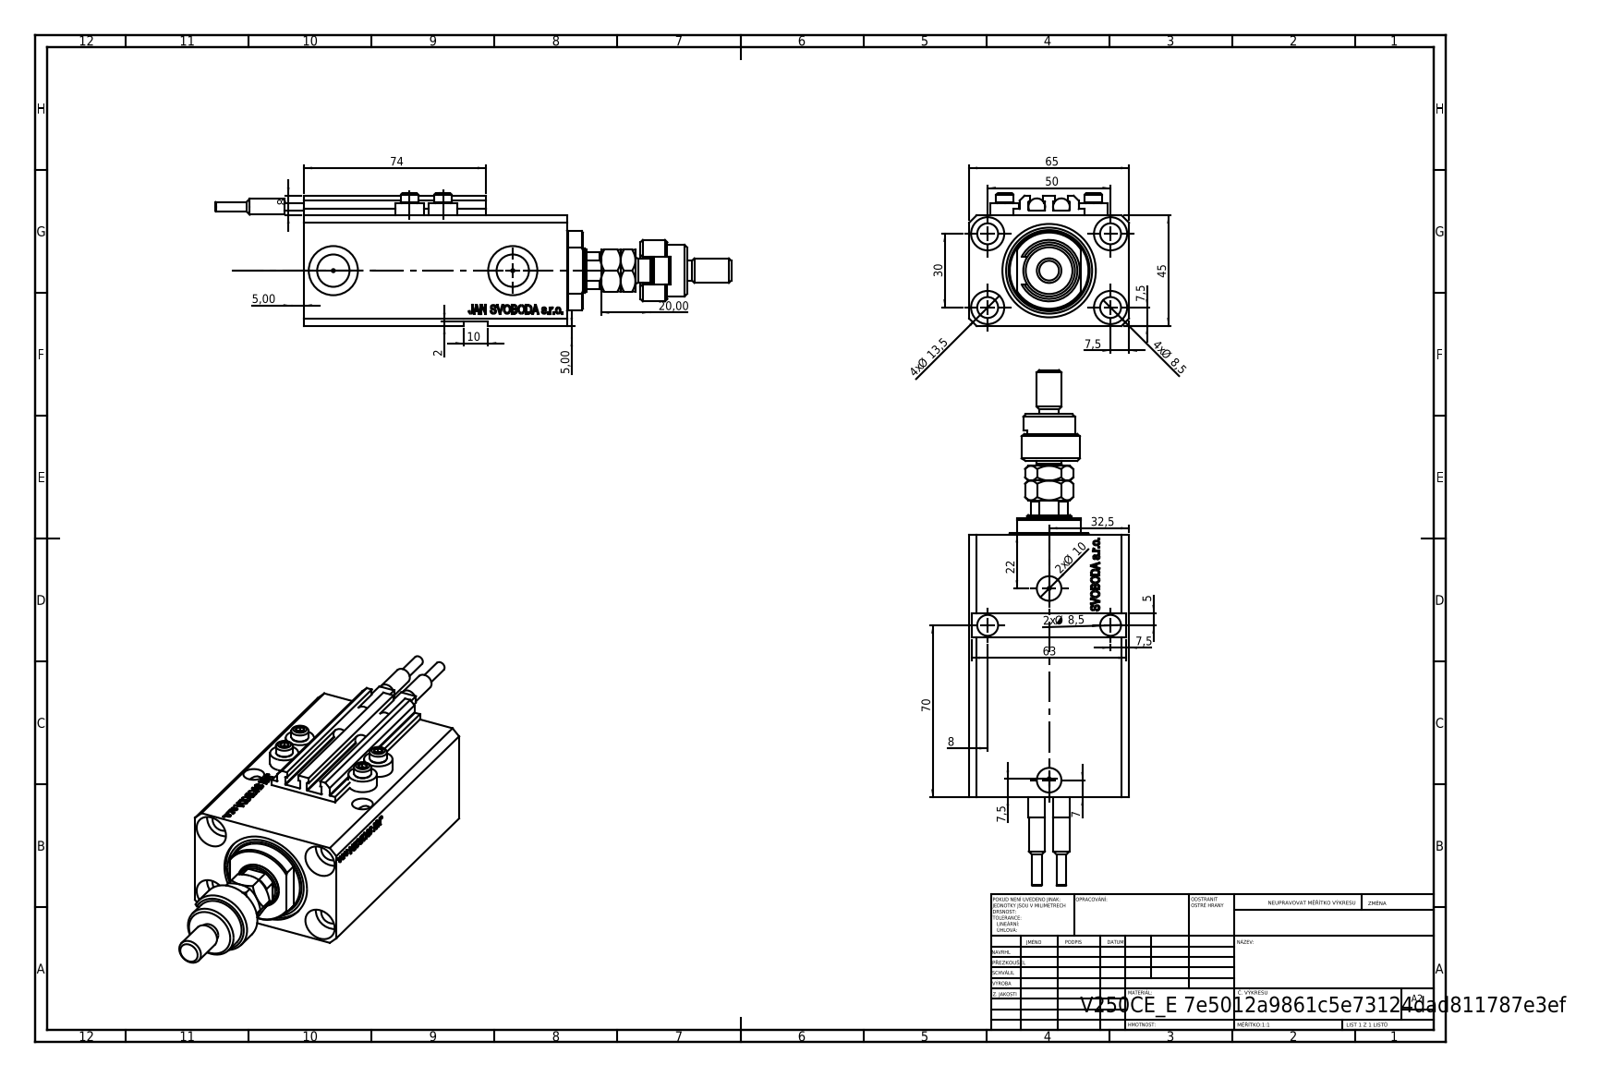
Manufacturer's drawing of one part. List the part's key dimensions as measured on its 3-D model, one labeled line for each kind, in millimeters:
Part name (STEP PRODUCT): SWITCH_V250CE; FEMALE_PART_FOR_DFA; MFA; ALLEN BOLT V250CE (+3 more)
STEP written by: SolidWorks 2019 (CONFIG_CONTROL_DESIGN)
Units: millimetres
Bodies: 12 solids, 1204 faces (571 planar, 151 cylindrical, 482 other)
Overall size (bounding box): 209.9 × 65 × 54
Volume: 292 227 mm³ · Surface area: 86 156 mm²
Round holes (diameter × count): ⌀8.5 ×7, ⌀1.25 ×4, ⌀4 ×4, ⌀13.5 ×4, ⌀10 ×2, ⌀13.16 ×2, ⌀20 ×2, ⌀18 ×1, ⌀38 ×1
Round bosses / shafts (diameter × count): ⌀11.6 ×4, ⌀7 ×4, ⌀6.8 ×2, ⌀6.5 ×2, ⌀4 ×2, ⌀25 ×1, ⌀21 ×1, ⌀16 ×1
Partial cylindrical surfaces — rounded edges, fillets, slot ends (radius × count): R0.2 ×10, R5.5 ×1, R8.5 ×1, R8.75 ×1, R16 ×1
Main face-to-face distances: 45, 65, 2, 81.9, 47, 3, 25.1, 107, 75, 10
Hole centre spacings: 29.15, 50, 13.6, 15.12, 27.89, 30, 33.62, 36
